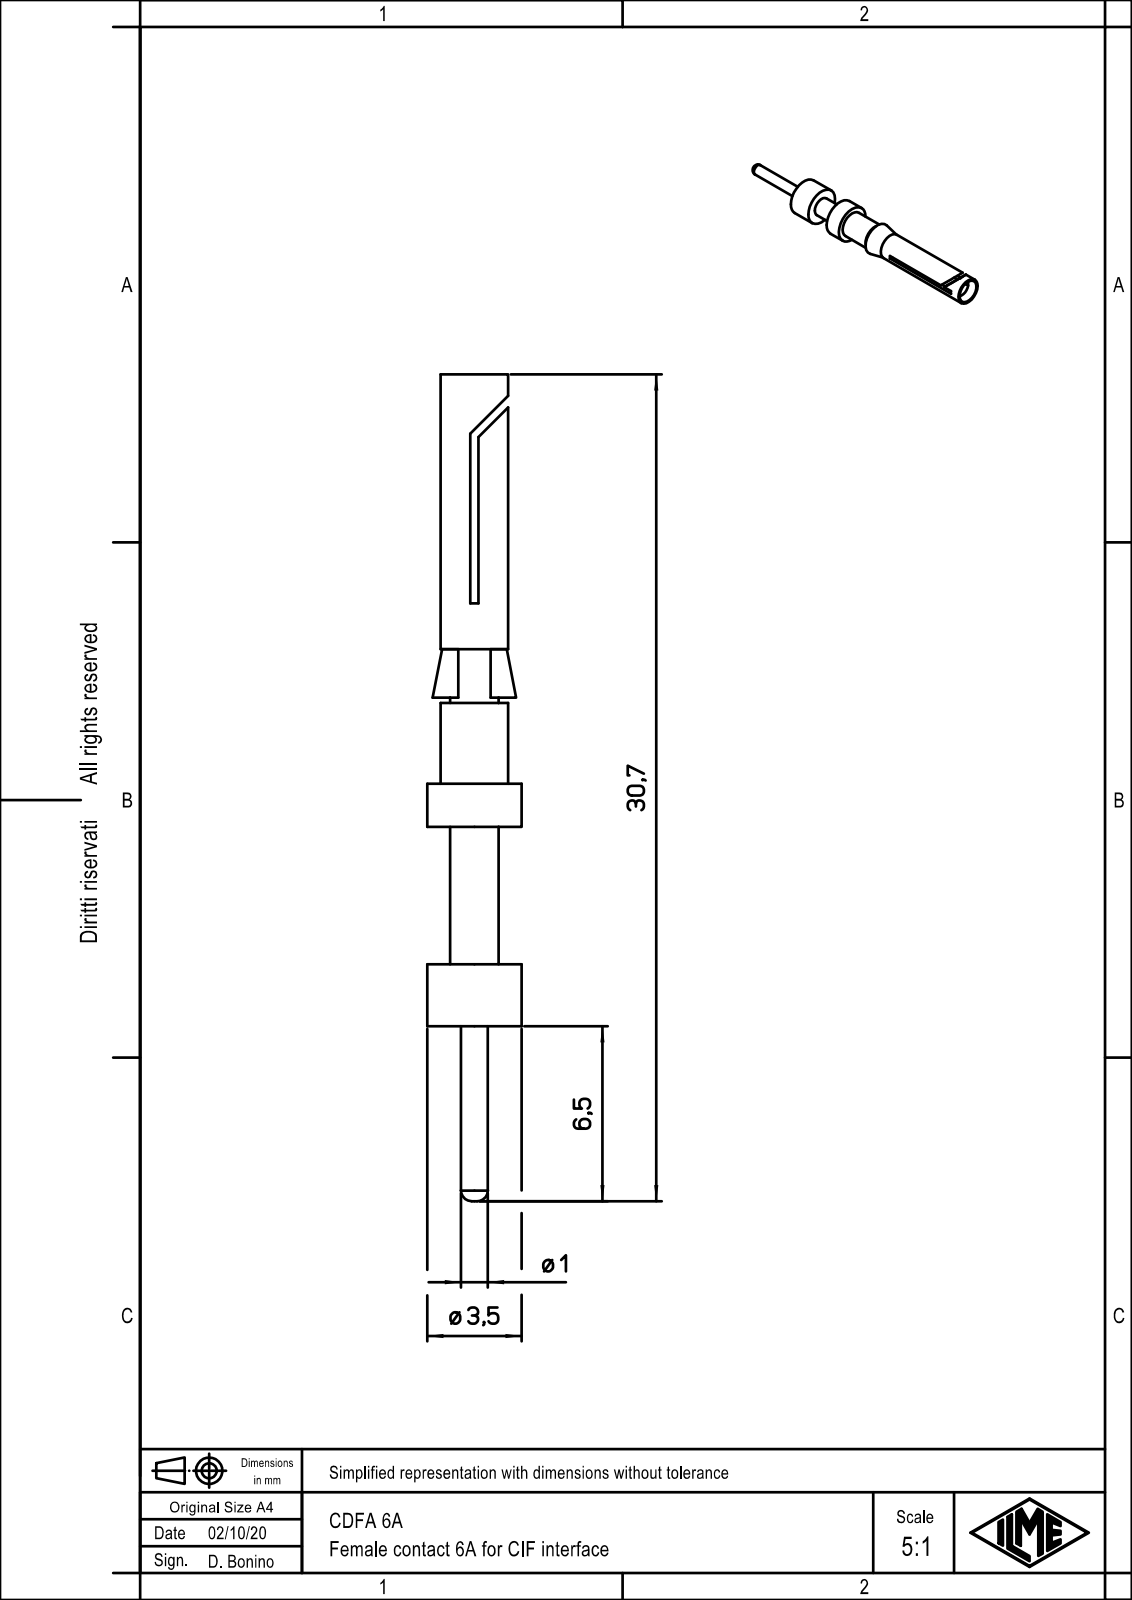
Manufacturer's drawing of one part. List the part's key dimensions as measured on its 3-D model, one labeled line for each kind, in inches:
Part name (STEP PRODUCT): CDFA_6A
STEP written by: PTC Creo Elements/Direct Modeling 19.0B 21-Mar-2015 (C) Parametric Technology GmbH (AUTOMOTIVE_DESIGN)
Units: inches
Bodies: 1 solid, 41 faces (18 planar, 19 cylindrical, 4 other)
Overall size (bounding box): 1.15 × 0.138 × 0.138
Volume: 0.007 in³ · Surface area: 0.46 in²
Round holes (diameter × count): ⌀0.065 ×1
Round bosses / shafts (diameter × count): ⌀0.138 ×1, ⌀0.126 ×1, ⌀0.098 ×1, ⌀0.071 ×1, ⌀0.039 ×1
Main face-to-face distances: 0.476, 0.291, 0.264, 0.185, 0.386, 0.201, 0.091, 0.122, 0.063, 0.354
